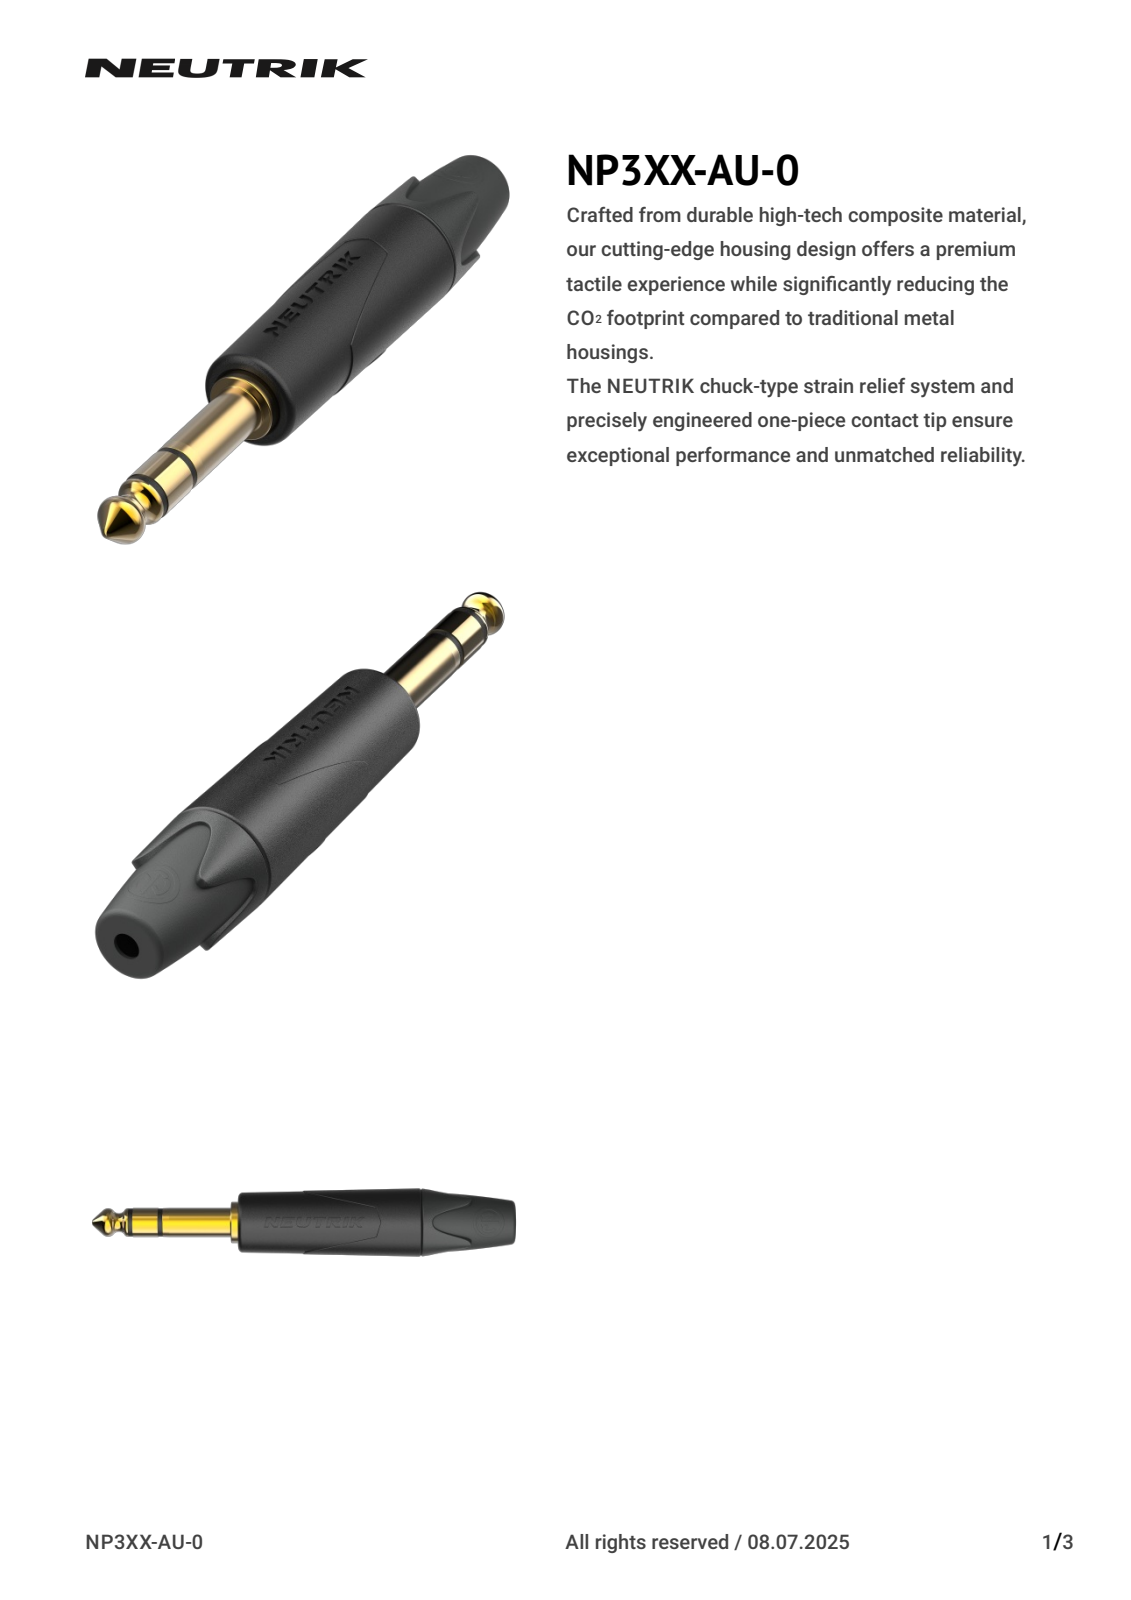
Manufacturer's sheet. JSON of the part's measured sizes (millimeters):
{"part_name": "30011563", "step_written_by": "CREO PARAMETRIC BY PTC INC, 2023424 (CONFIG_CONTROL_DESIGN)", "units": "millimeters", "bodies": {"solids": 1, "faces": 299, "planar": 79, "cylindrical": 40, "other": 180}, "overall_size": [92.61, 14.86, 14.86], "volume_mm3": 9488, "surface_area_mm2": 3438, "round_holes": [[3.5, 1]], "round_bosses_or_shafts": [[10.16, 1], [8.95, 1], [6.29, 1], [6.15, 1], [6.1, 1]], "partial_cylinders_radius": [[0.46, 9], [0.15, 2], [0.35, 1], [0.44, 1], [0.88, 1], [1.1, 1], [2.54, 1], [3.46, 1]], "face_to_face_distances": [60.51, 62.08, 1.57, 0.5, 60.01, 61.58, 20.51, 20.01, 40, 41.57]}
